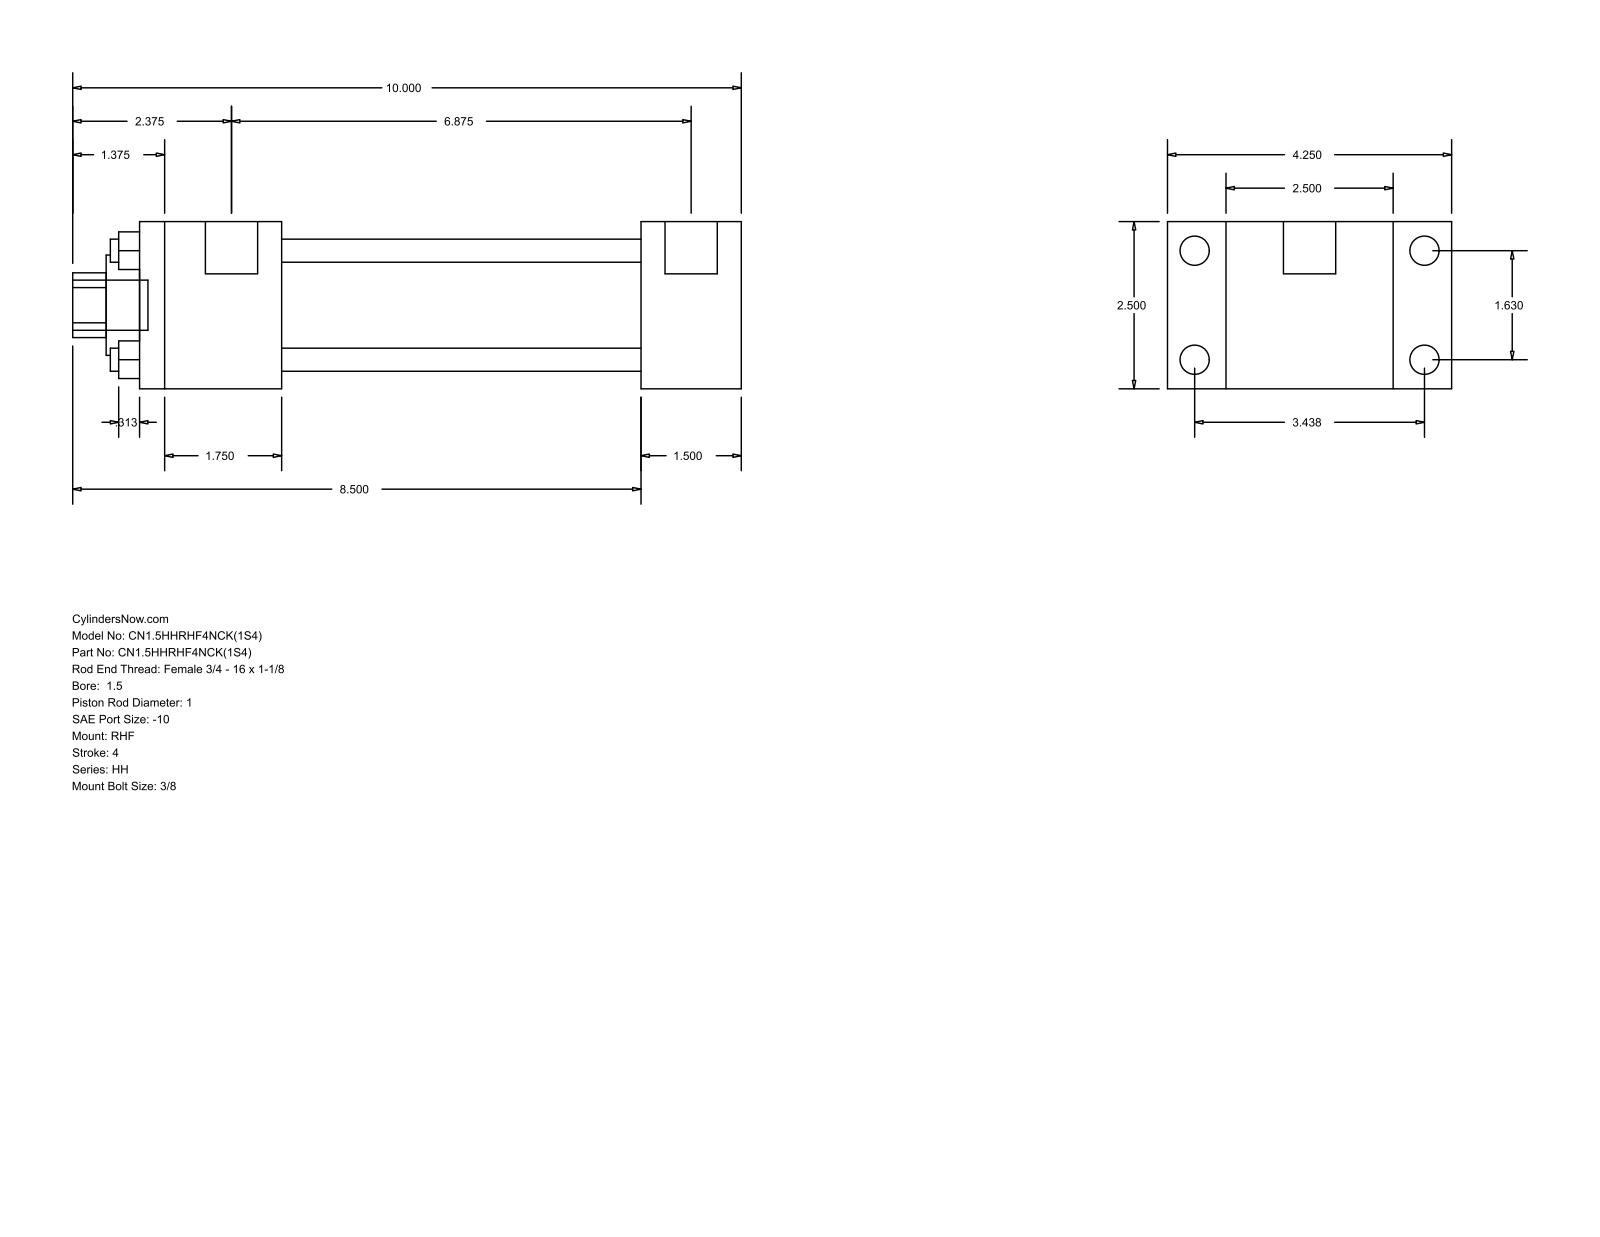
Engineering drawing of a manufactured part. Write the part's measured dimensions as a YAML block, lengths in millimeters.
part_name: "HH_RHF__0150_1"
step_written_by: "GSSL Pune (CONFIG_CONTROL_DESIGN)"
units: millimeters
bodies: {solids: 0, faces: 88, planar: 60, cylindrical: 28, other: 0}
overall_size: [254, 107.95, 63.5]
round_holes:
  - {diameter: 8.76, count: 4}
  - {diameter: 25.4, count: 1}
  - {diameter: 38.1, count: 1}
  - {diameter: 44.45, count: 1}
round_bosses_or_shafts:
  - {diameter: 11.13, count: 4}
  - {diameter: 5.56, count: 4}
  - {diameter: 19.84, count: 2}
  - {diameter: 19.05, count: 1}
partial_cylinders:
  - {radius: 12.29, count: 1}
face_to_face_distances: [63.5, 22.23, 85.73, 38.1, 107.96, 136.52, 174.62, 53.98, 190.5, 228.6]
hole_center_spacings: [29.27, 41.4, 58.55]
